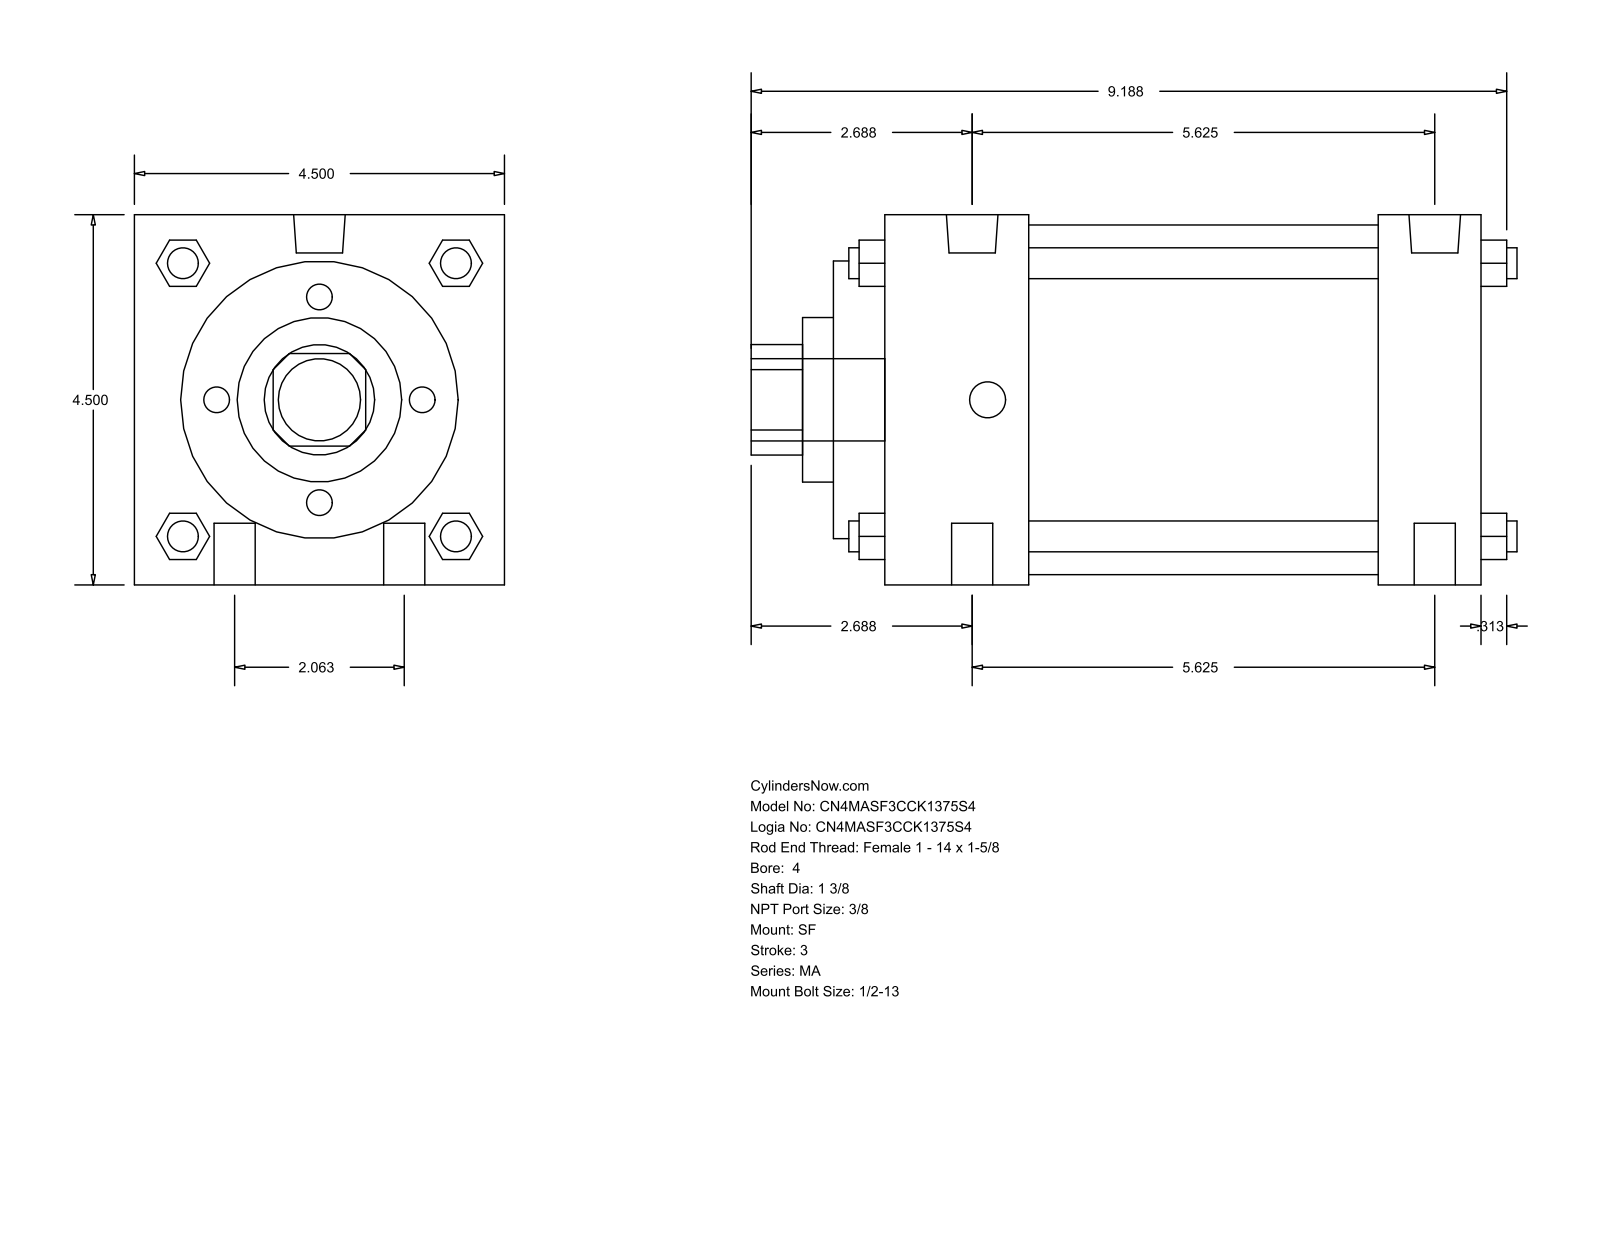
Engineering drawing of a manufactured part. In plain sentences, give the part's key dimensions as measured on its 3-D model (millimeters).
The part is named "MA_SF__0400_1.375". Its 3-D file was written by "GSSL Pune (CONFIG_CONTROL_DESIGN)". It is 0 solids with 126 faces: 95 planar, 31 cylindrical and 0 other. Overall it measures 236.54 by 114.3 by 114.3 millimeters. Round holes: 1 of diameter 34.92, 1 of diameter 50.8, 1 of diameter 85.72, 1 of diameter 107.95. Round bosses or shafts: 4 of diameter 12.7, 4 of diameter 9.53, 2 of diameter 15.93, 2 of diameter 11.11, 1 of diameter 25.4. Partial cylindrical surfaces (rounded edges, fillets, slot ends): 1 of radius 17.06. The main face-to-face distances are 114.3, 184.16, 15.87, 200.03, 168.28, 152.41, 31.75, 60.32, 44.45, 107.96.
